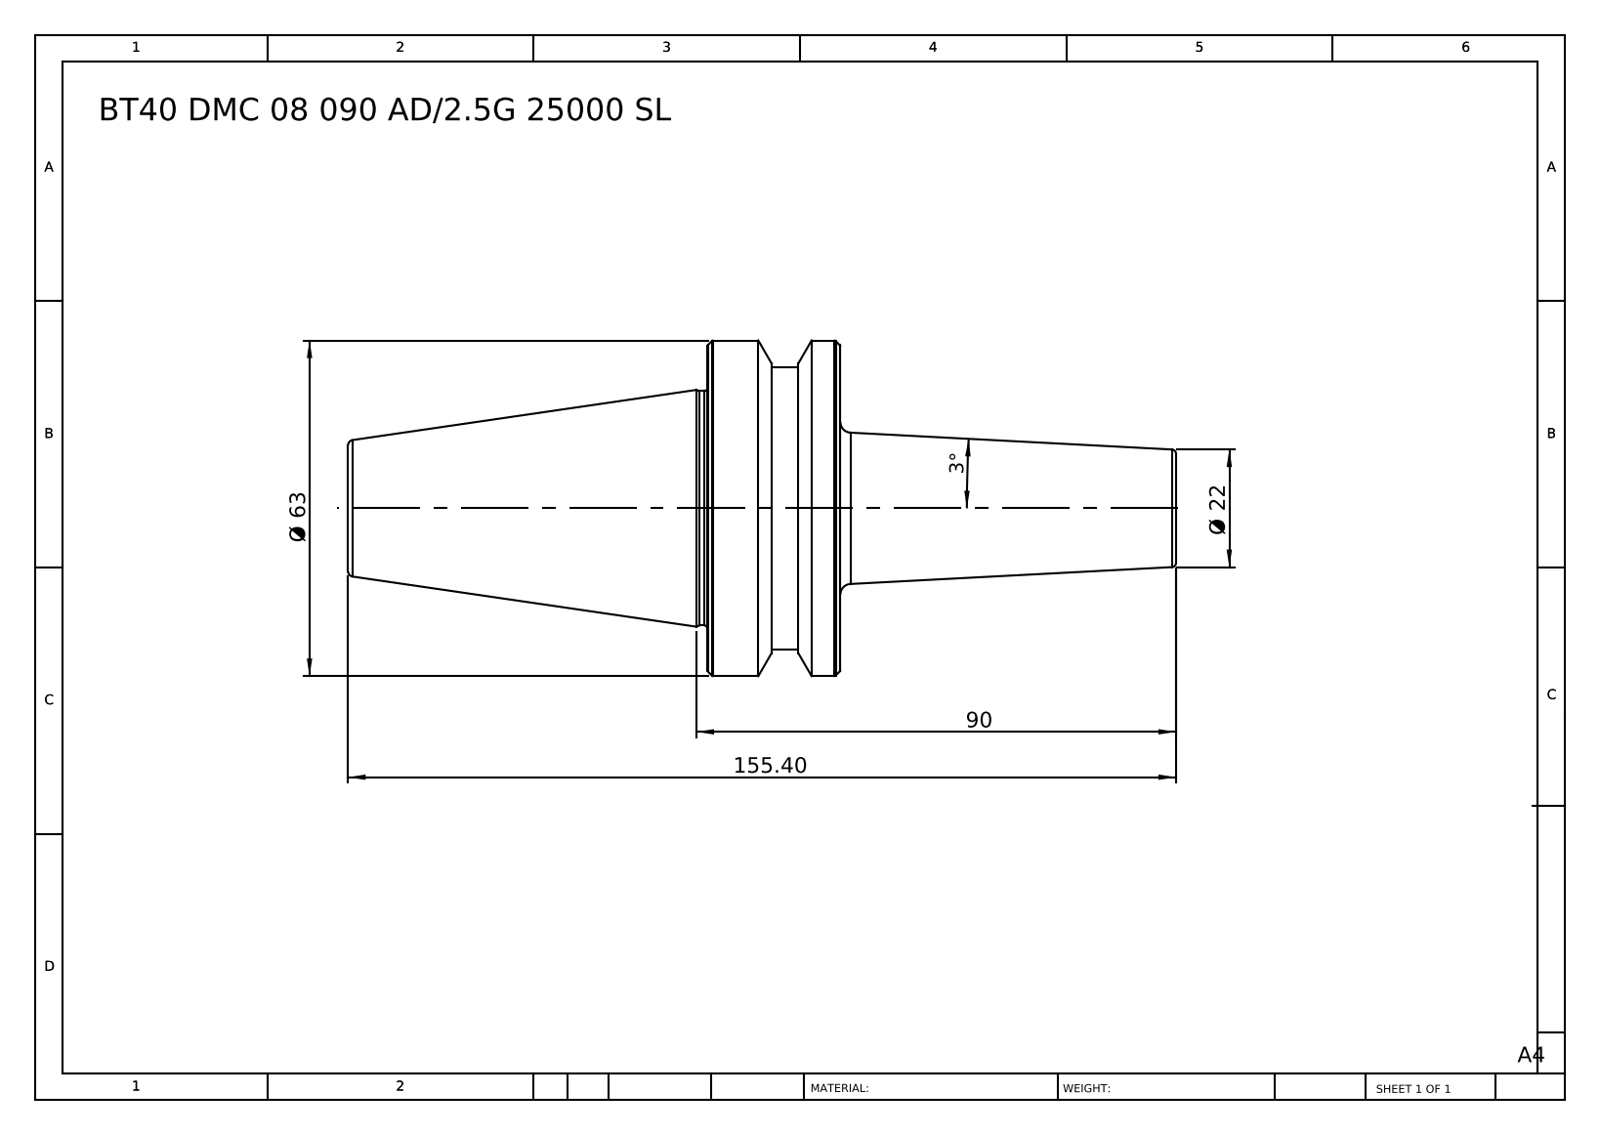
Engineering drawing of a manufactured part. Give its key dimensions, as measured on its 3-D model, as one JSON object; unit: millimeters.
{"part_name": "BT40 DMC 08 090 AD-2.5G 25000 SL", "step_written_by": "SolidWorks 2014 (CONFIG_CONTROL_DESIGN)", "units": "millimeters", "bodies": {"solids": 1, "faces": 44, "planar": 6, "cylindrical": 8, "other": 30}, "overall_size": [155.4, 63, 63], "volume_mm3": 170260, "surface_area_mm2": 22985, "round_bosses_or_shafts": [[63, 1], [53, 1], [44, 1]], "face_to_face_distances": [25, 92.4, 67.4, 63, 88, 155.4, 70.9, 7.9, 17.1, 84.5]}
